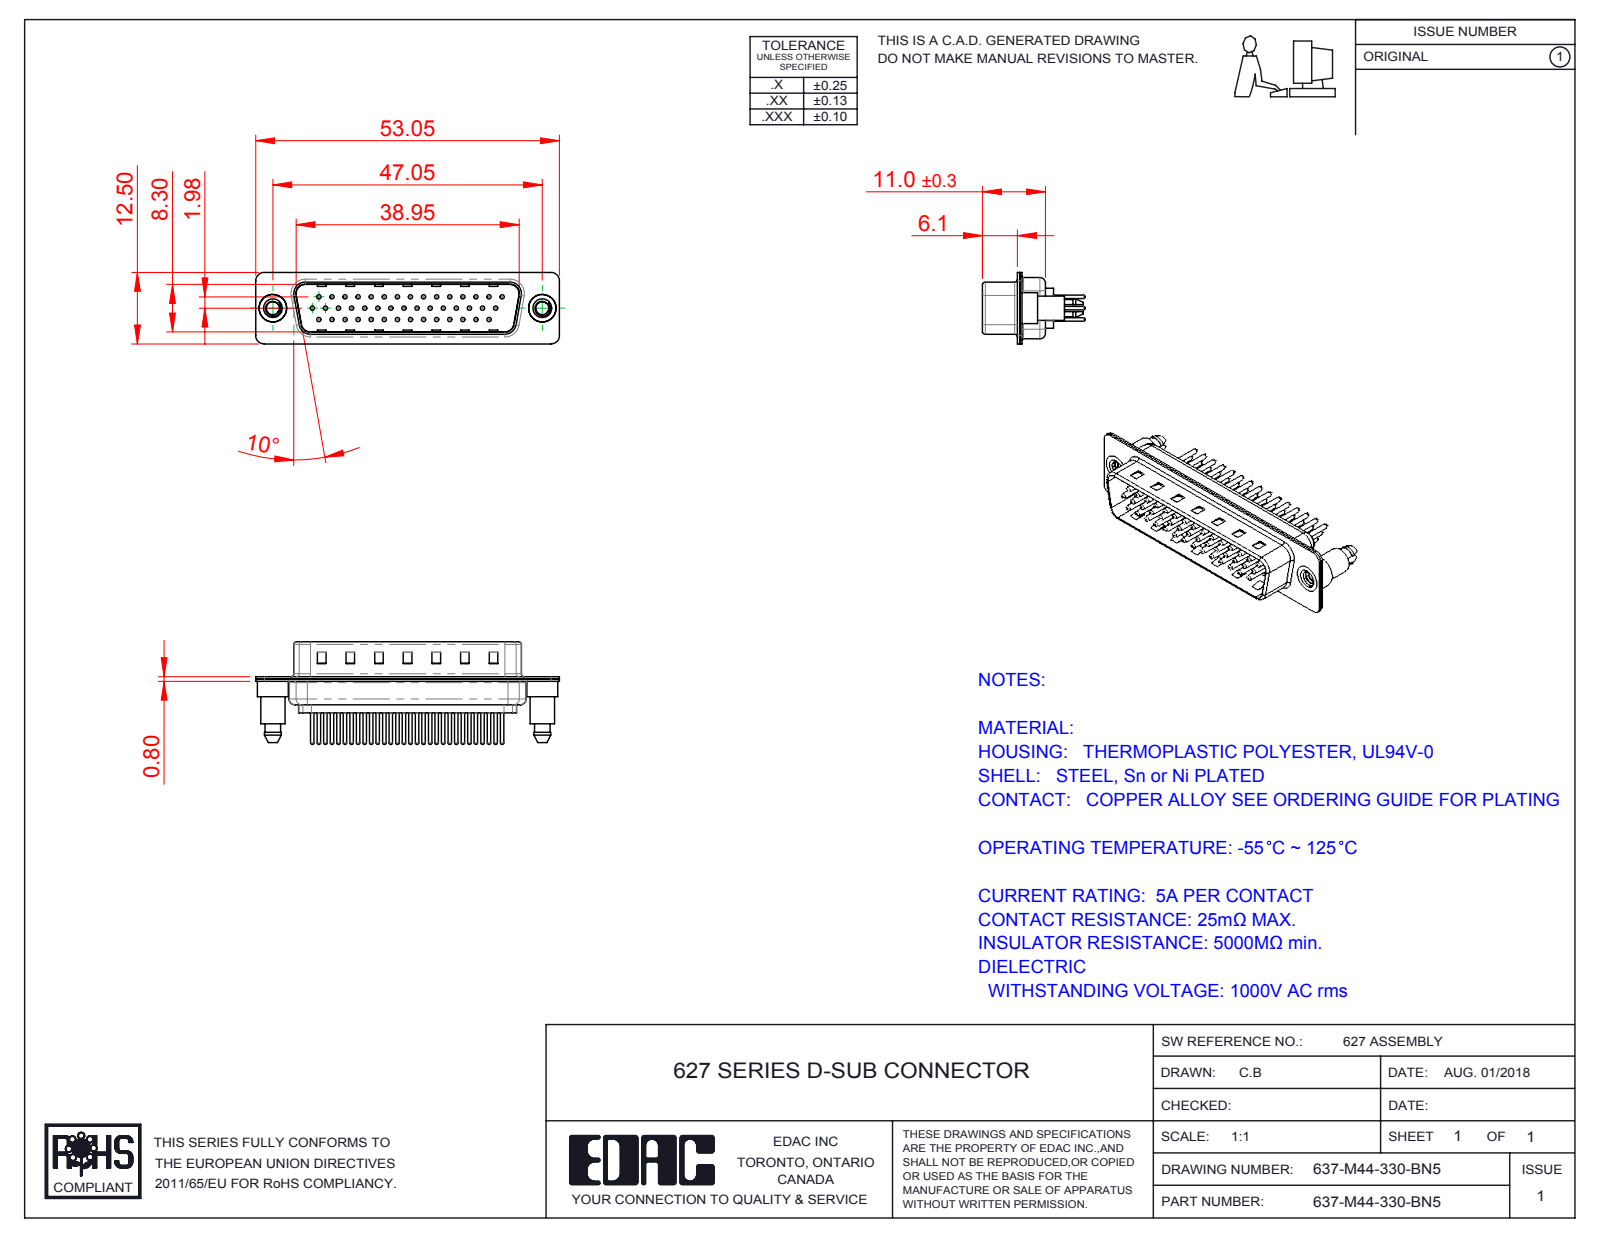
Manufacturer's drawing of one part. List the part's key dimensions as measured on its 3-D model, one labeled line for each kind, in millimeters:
Part name (STEP PRODUCT): 637M 4-40 Threaded Boardlock; 637M Housing_44 Contacts; 637M Shell Rear_44 Contacts; 637M Contact Row 2_30 (+4 more)
STEP written by: SolidWorks 2016 (CONFIG_CONTROL_DESIGN)
Units: millimetres
Bodies: 49 solids, 2054 faces (495 planar, 785 cylindrical, 774 other)
Overall size (bounding box): 53.05 × 17.9 × 12.5
Volume: 2 962 mm³ · Surface area: 8 800 mm²
Round holes (diameter × count): ⌀0.75 ×44, ⌀1.6 ×44, ⌀2 ×44, ⌀2.26 ×2, ⌀4 ×2, ⌀4.8 ×2
Round bosses / shafts (diameter × count): ⌀1.5 ×44, ⌀0.6 ×44, ⌀2 ×3, ⌀0.75 ×3, ⌀5.4 ×2, ⌀4.9 ×2, ⌀4.25 ×2
Partial cylindrical surfaces — rounded edges, fillets, slot ends (radius × count): R1.5 ×18, R2 ×12, R1.6 ×10, R0.5 ×8, R0.25 ×4, R0.6 ×4, R0.65 ×4, R0.9 ×4
Main face-to-face distances: 0.4, 0.8, 9.5, 9.1, 8.7, 9.9, 6.3, 0.75, 1.1, 0.35
Hole centre spacings: 2.28, 3.96, 2.29, 4.57, 8.24, 6.86, 11.43, 14.99
